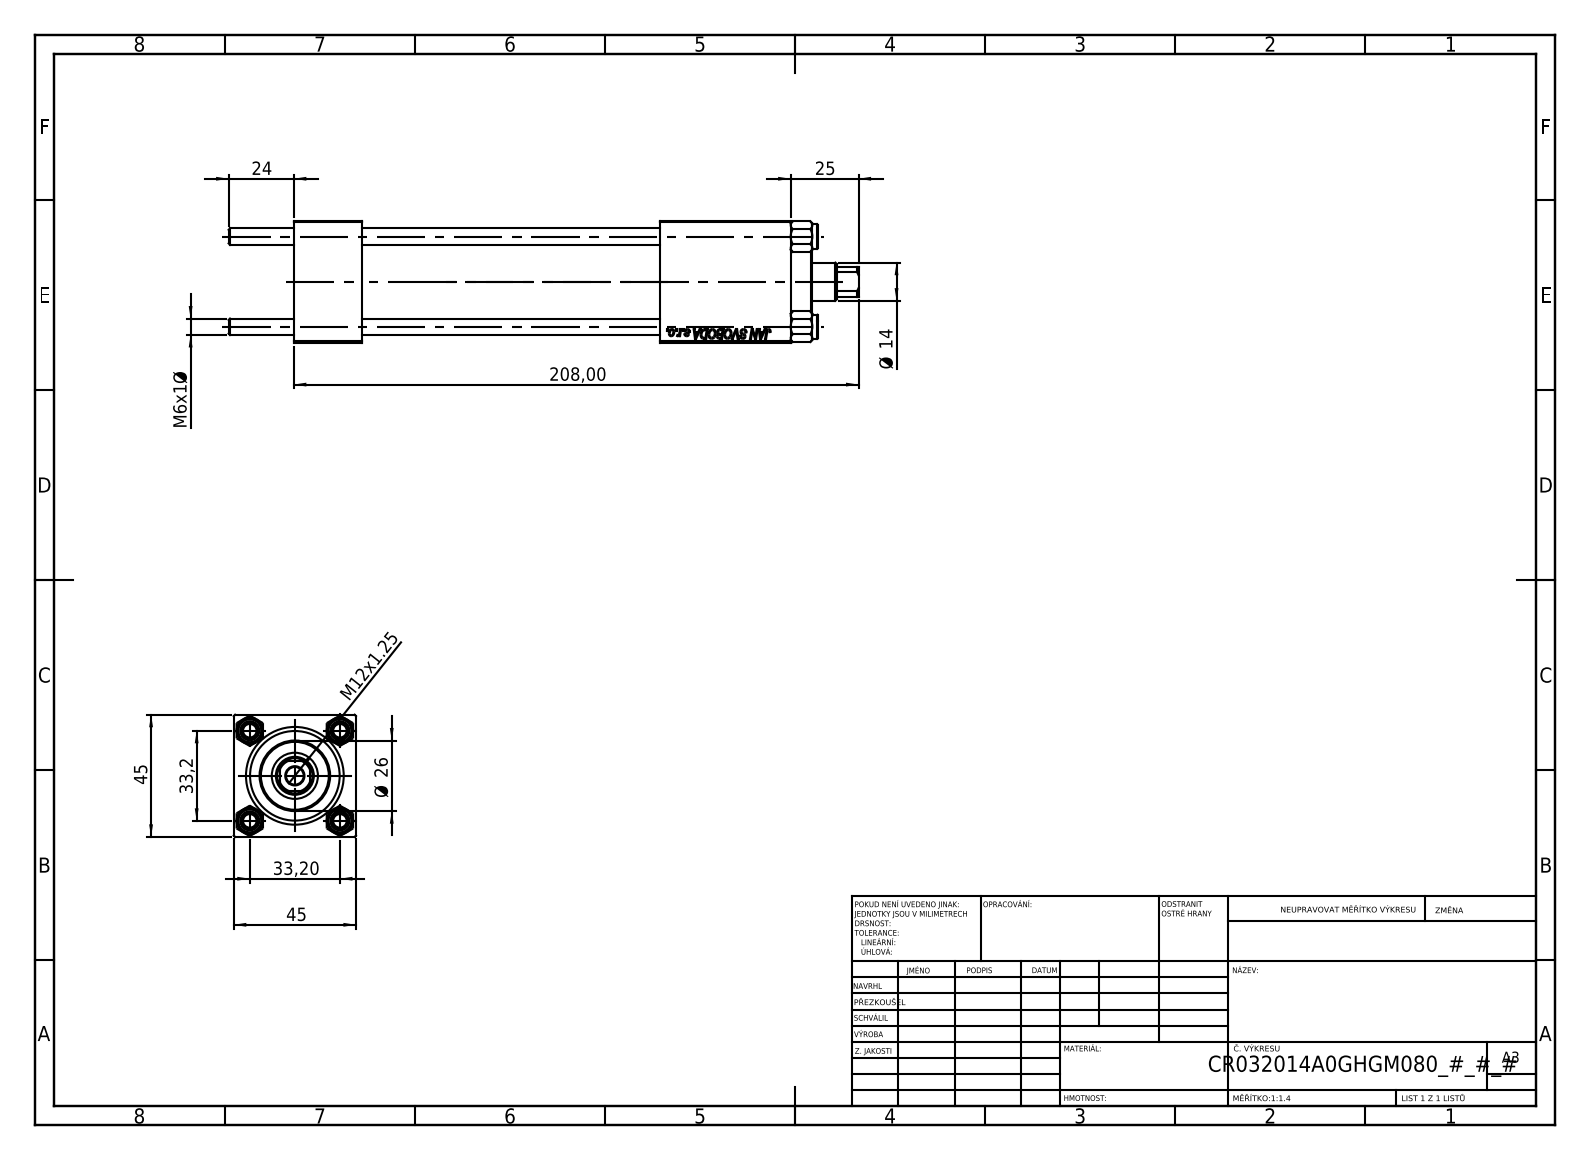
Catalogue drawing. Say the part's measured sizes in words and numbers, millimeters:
The part is named "CR025_012_A_0_G_A_G_M_020_+#_##_TYCINKA; V215CR_VCP; V215_VC_A; V215CR_BODY_A (+1 more)". Its 3-D file was written by "SolidWorks 2019 (CONFIG_CONTROL_DESIGN)". It is 11 solids with 1133 faces: 519 planar, 78 cylindrical and 536 other. Overall it measures 232 by 45 by 45 millimeters. Its volume is 234 126 cubic millimeters and its surface area 93 181 square millimeters. Round holes: 4 of diameter 6, 2 of diameter 7, 2 of diameter 13.16, 2 of diameter 20, 1 of diameter 6.5, 1 of diameter 14, 1 of diameter 17, 1 of diameter 24, 1 of diameter 32, 1 of diameter 33. Round bosses or shafts: 4 of diameter 9, 1 of diameter 38, 1 of diameter 26. Partial cylindrical surfaces (rounded edges, fillets, slot ends): 1 of radius 6.5. The main face-to-face distances are 45, 25, 183, 158, 135, 110, 48, 154.3, 129.3, 19.3. The hole center spacings are 23.48, 33.2, 46.95, 135.5.
